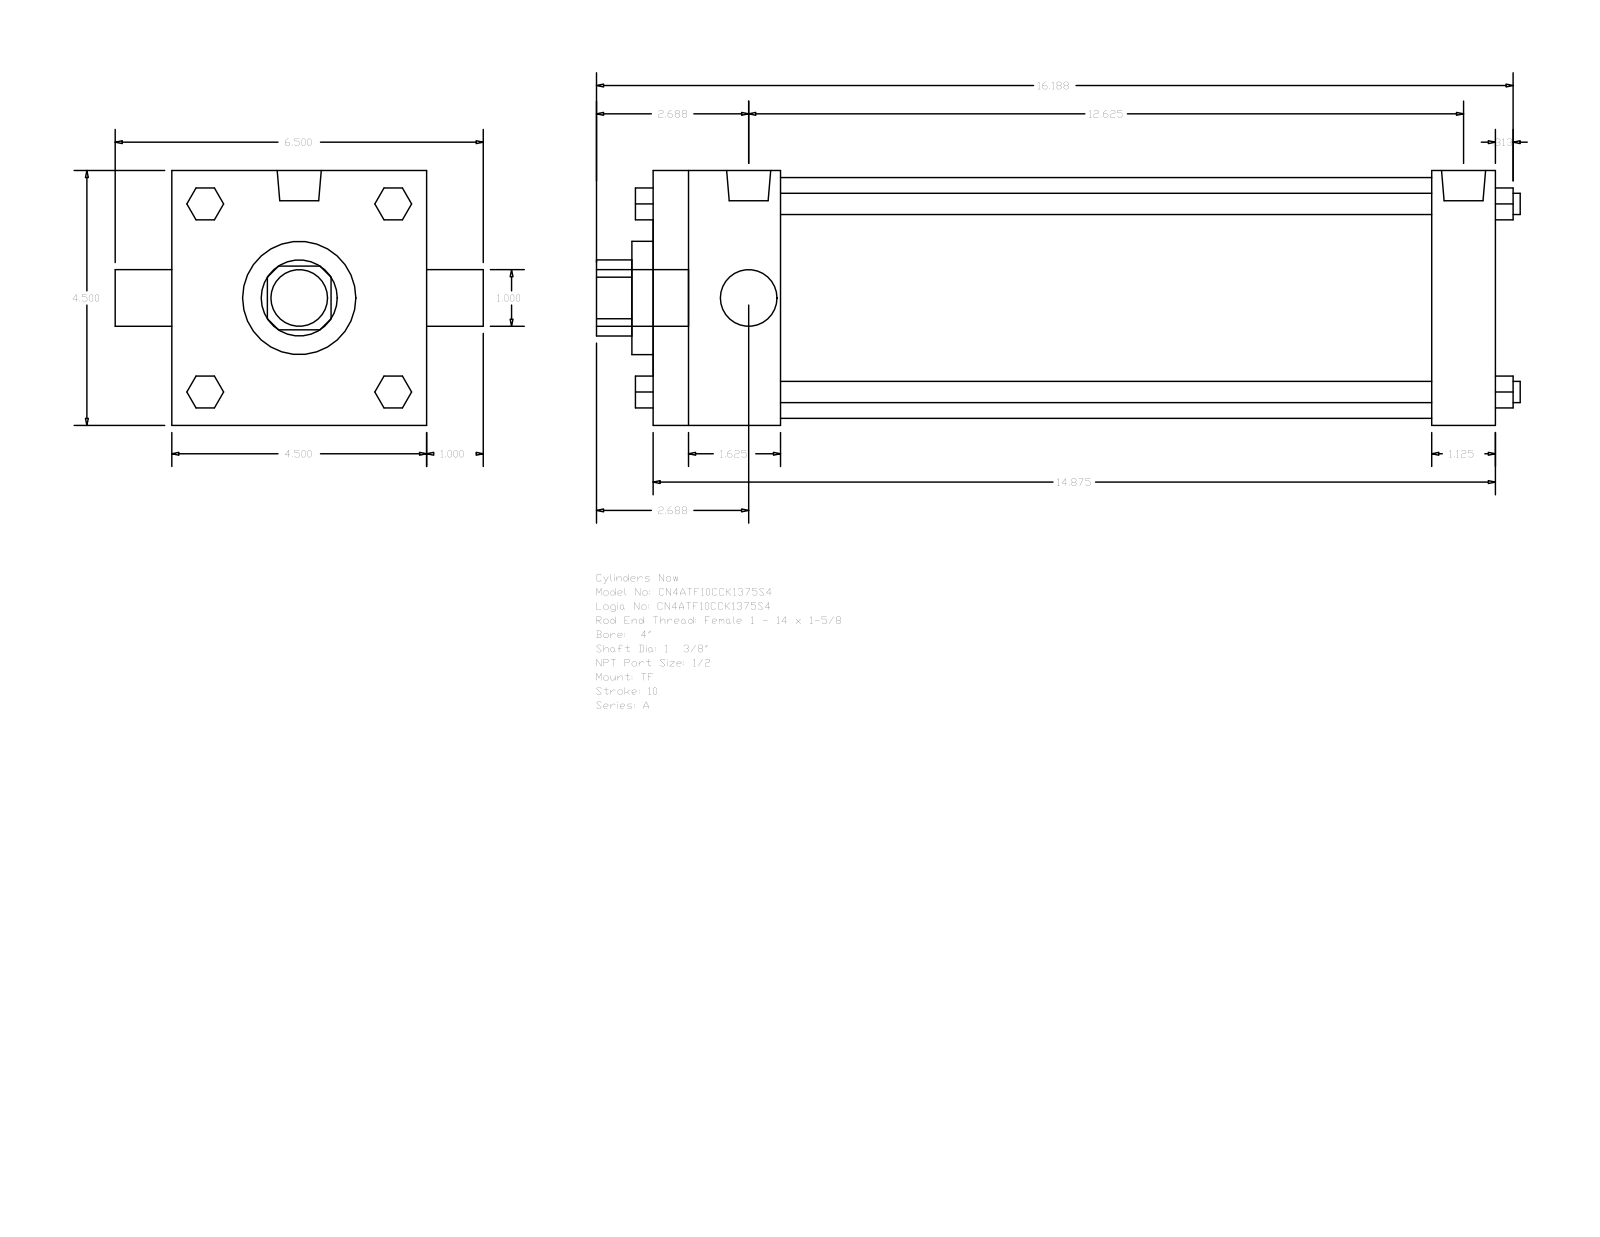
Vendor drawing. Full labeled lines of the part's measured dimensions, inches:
Part name (STEP PRODUCT): A_TF__0400_1.375
STEP written by: GSSL Pune (CONFIG_CONTROL_DESIGN)
Units: inches
Bodies: 0 solids, 120 faces (92 planar, 28 cylindrical, 0 other)
Overall size (bounding box): 16.313 × 6.5 × 4.5
Round holes (diameter × count): ⌀1 ×1, ⌀1.375 ×1, ⌀2 ×1, ⌀4.25 ×1
Round bosses / shafts (diameter × count): ⌀0.375 ×4, ⌀0.344 ×3, ⌀0.778 ×2, ⌀1 ×1
Partial cylindrical surfaces — rounded edges, fillets, slot ends (radius × count): R0.672 ×1
Main face-to-face distances: 4.5, 14.875, 1.125, 13.75, 2.25, 11.5, 12.625, 0.563, 1, 0.375
